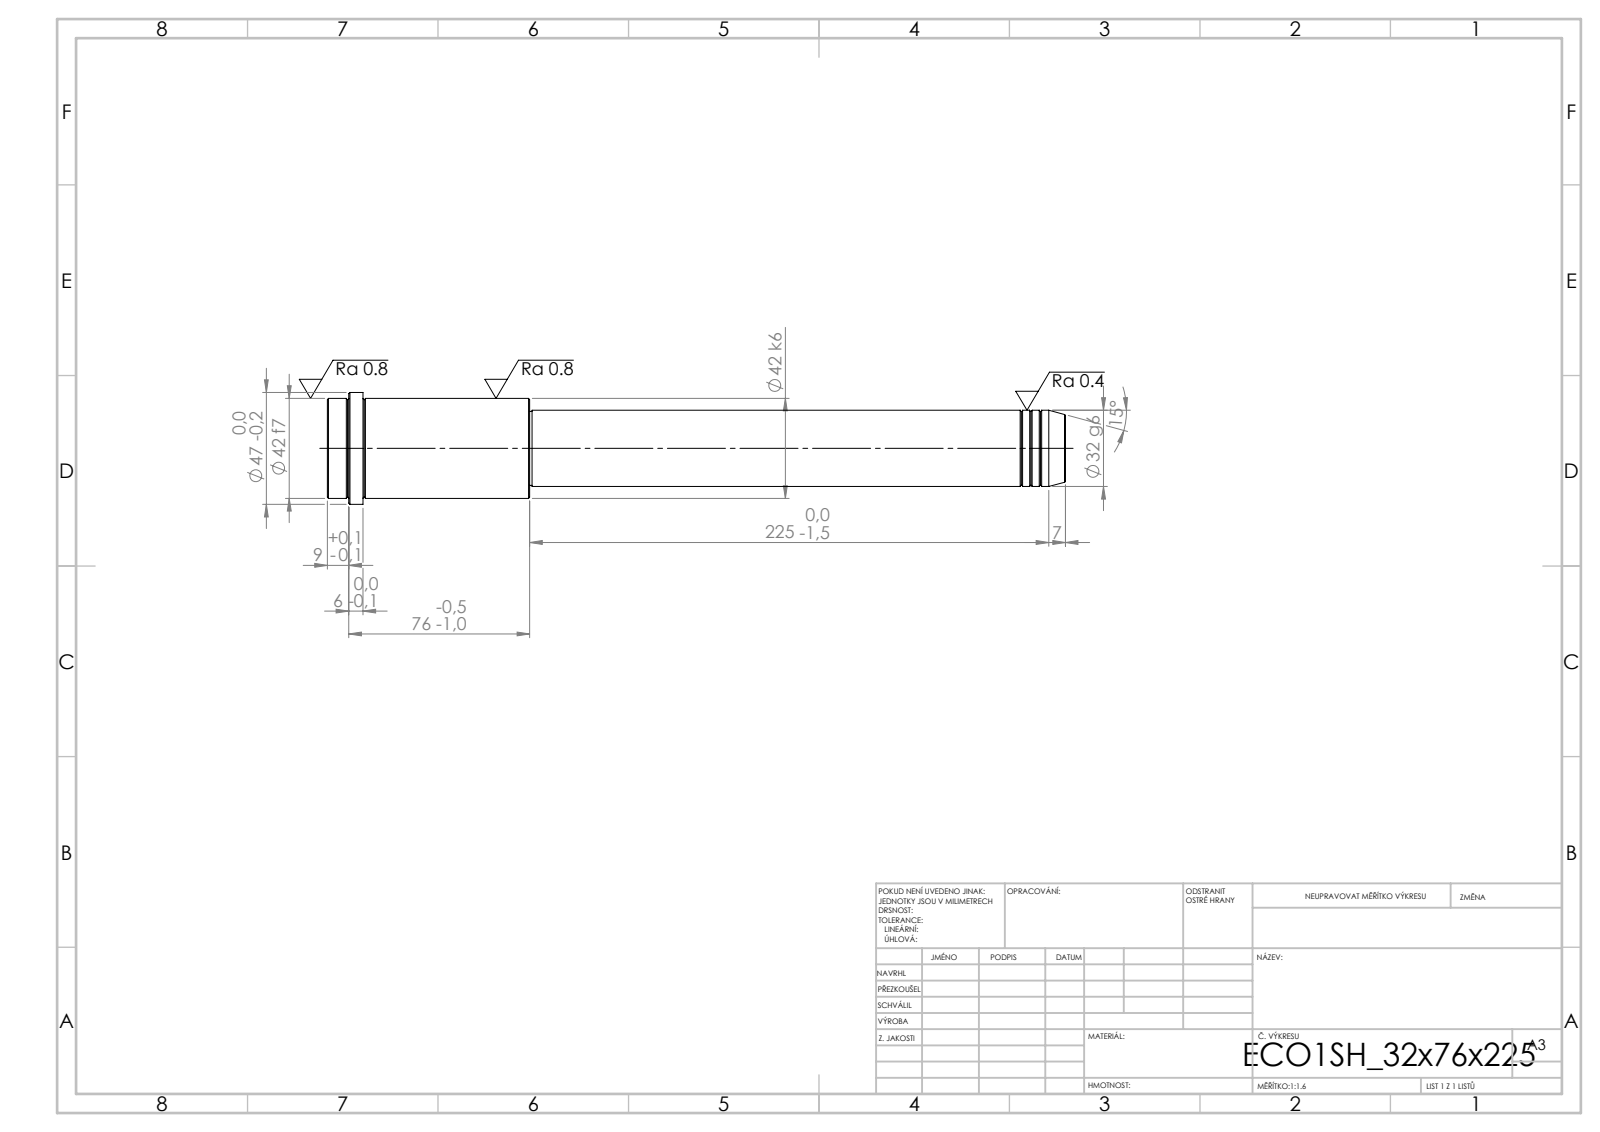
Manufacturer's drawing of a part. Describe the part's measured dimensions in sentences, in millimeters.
Its 3-D file was written by "SolidWorks 2019 (CONFIG_CONTROL_DESIGN)". It is 1 solid with 52 faces: 6 planar, 16 cylindrical and 30 other. Overall it measures 310 by 47 by 47 millimeters. Its volume is 299 859 cubic millimeters and its surface area 37 475 square millimeters. Round bosses or shafts: 1 of diameter 47, 1 of diameter 42, 1 of diameter 32, 1 of diameter 31. The main face-to-face distances are 310, 225, 85, 295, 70, 15, 301, 76, 6, 9.
